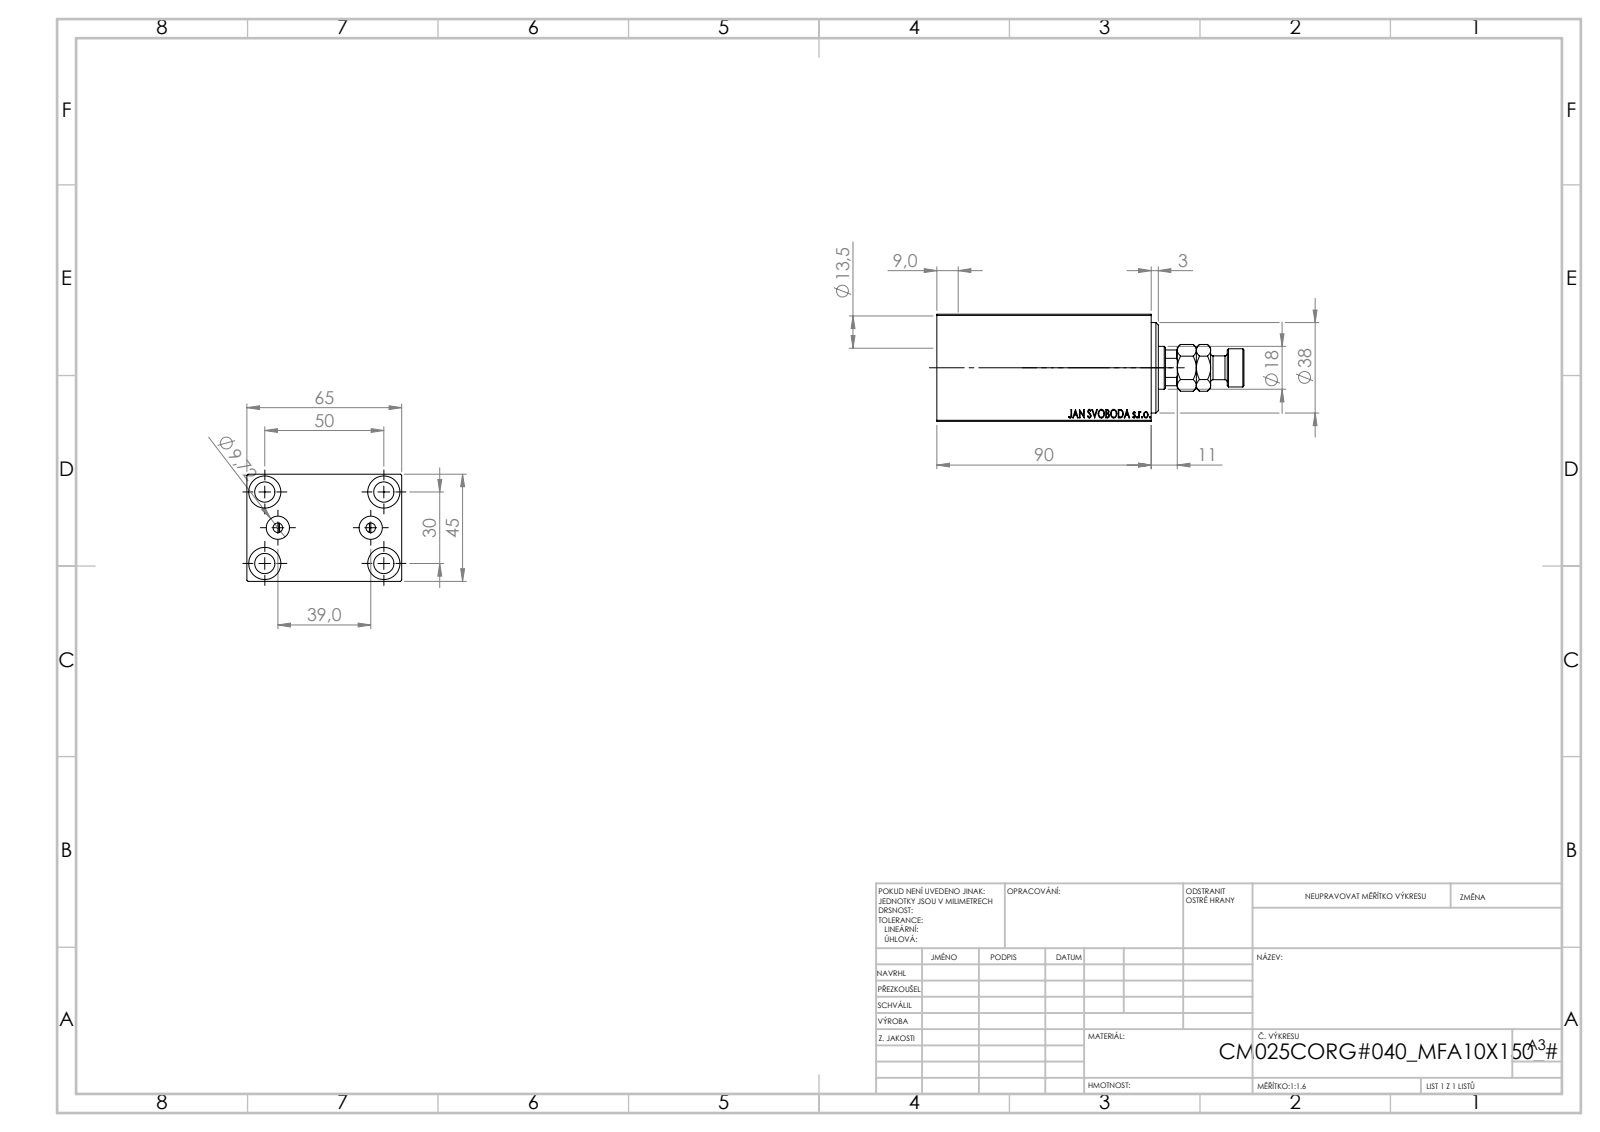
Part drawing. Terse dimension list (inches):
name: V450CM_C_VCP; V450CM_C_Body; MFA; V450CM_VC_B
written by: SolidWorks 2019 (CONFIG_CONTROL_DESIGN)
unit: in
bodies: 4 solids, 910 faces (424 planar, 60 cylindrical, 426 other)
size: 5.079 × 2.559 × 1.772
volume: 14.23 in³; area: 90.99 in²
holes: 5× ⌀0.335, 4× ⌀0.531, 2× ⌀0.157, 2× ⌀0.383, 1× ⌀0.709, 1× ⌀0.846, 1× ⌀0.984, 1× ⌀1.063, 1× ⌀1.496
bosses: 1× ⌀0.63, 1× ⌀0.394
rounds: 1× R0.335
face distances: 1.772, 2.559, 0.236, 3.11, 3.307, 3.543, 3.346, 0.197, 0.118, 0.315
hole spacings: 0.629, 1.148, 1.849, 0.768, 1.181, 1.969, 2.296, 1.535
